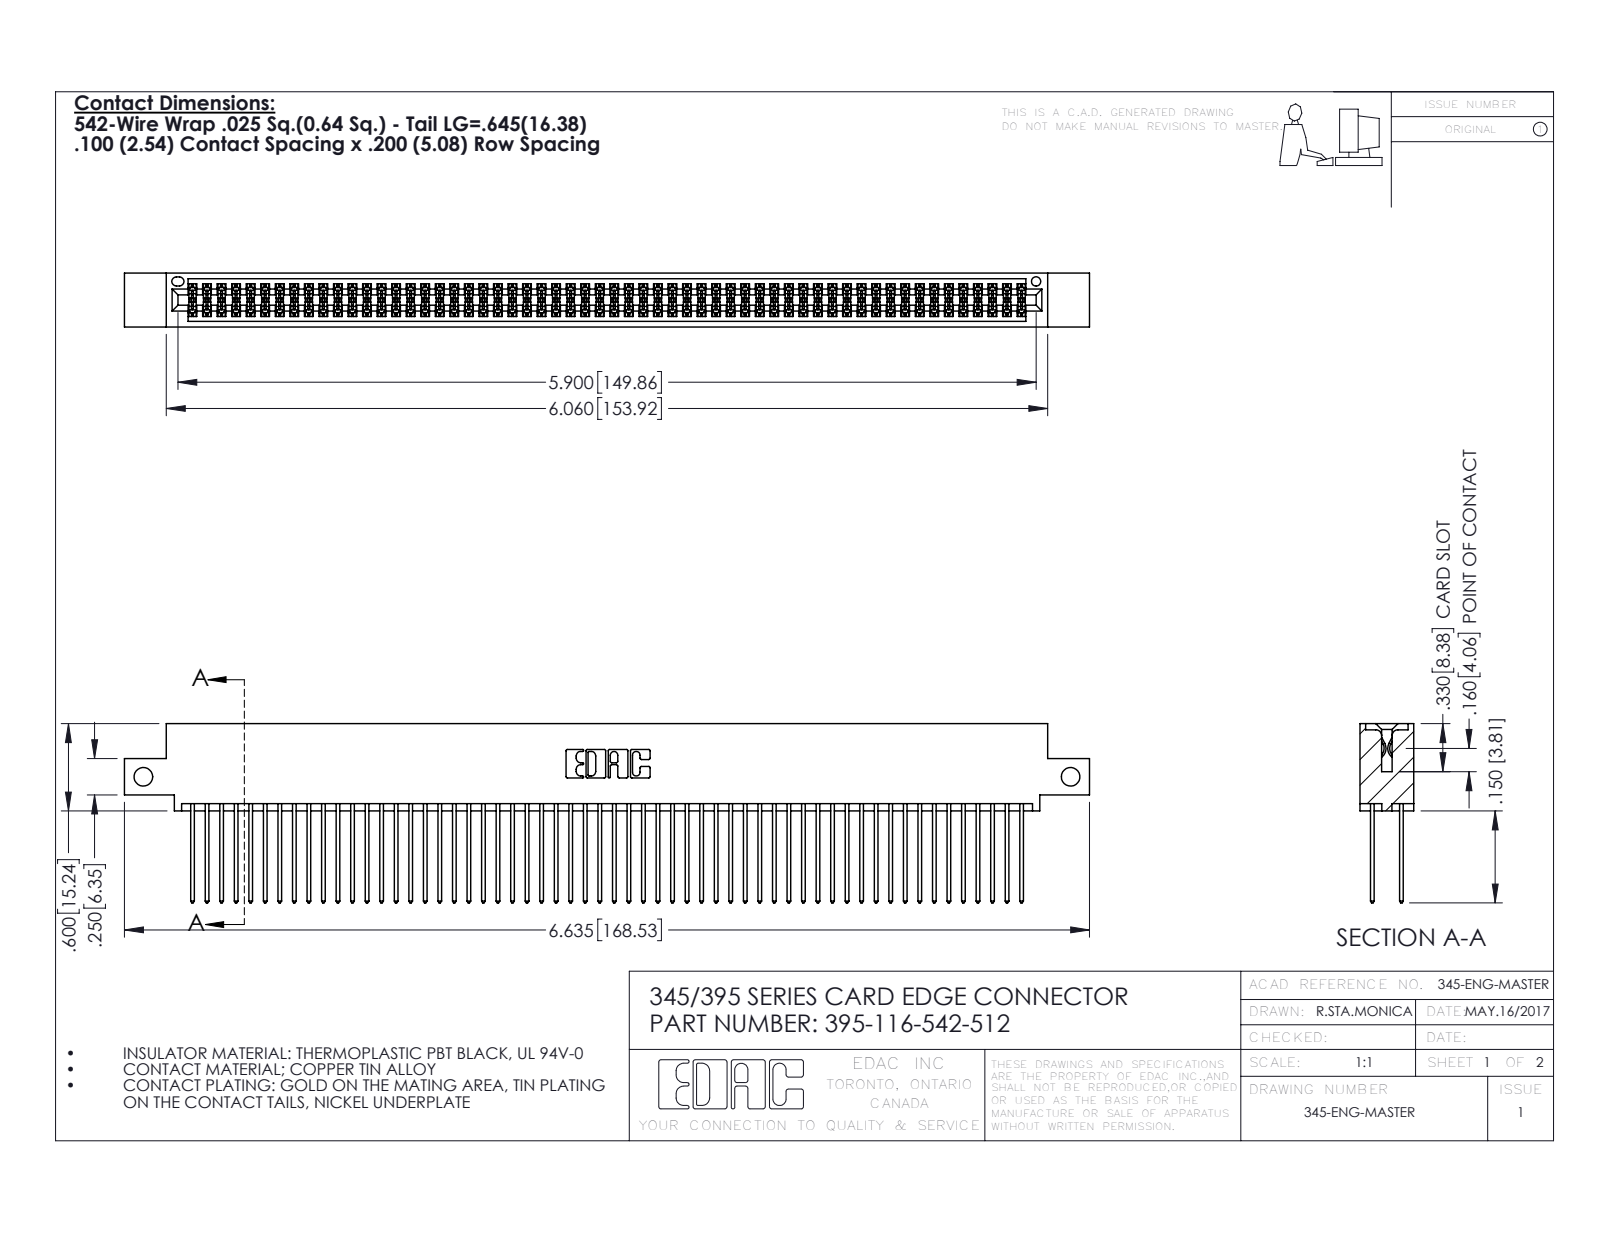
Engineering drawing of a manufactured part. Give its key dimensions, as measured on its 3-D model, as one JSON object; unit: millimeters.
{"part_name": "395-116-542-512; 345-292-001_345-293-142; 345 Part_0.110 Offset - Side Mount", "step_written_by": "SolidWorks 2016 (CONFIG_CONTROL_DESIGN)", "units": "millimeters", "bodies": {"solids": 117, "faces": 5930, "planar": 3912, "cylindrical": 2018, "other": 0}, "overall_size": [168.5, 31.3, 9.4], "volume_mm3": 16900, "surface_area_mm2": 27770, "round_holes": [[3.3, 2], [1.6, 1]], "partial_cylinders_radius": [[0.2, 174], [0.3, 116], [0.3, 22], [0.2, 6], [0.8, 6], [0.7, 3], [0.4, 2], [0.5, 2]], "face_to_face_distances": [7.6, 1.8, 5.1, 2.5, 6.9, 0.6, 5.7, 9.4, 4.4, 3.8], "hole_center_spacings": [161.9]}
